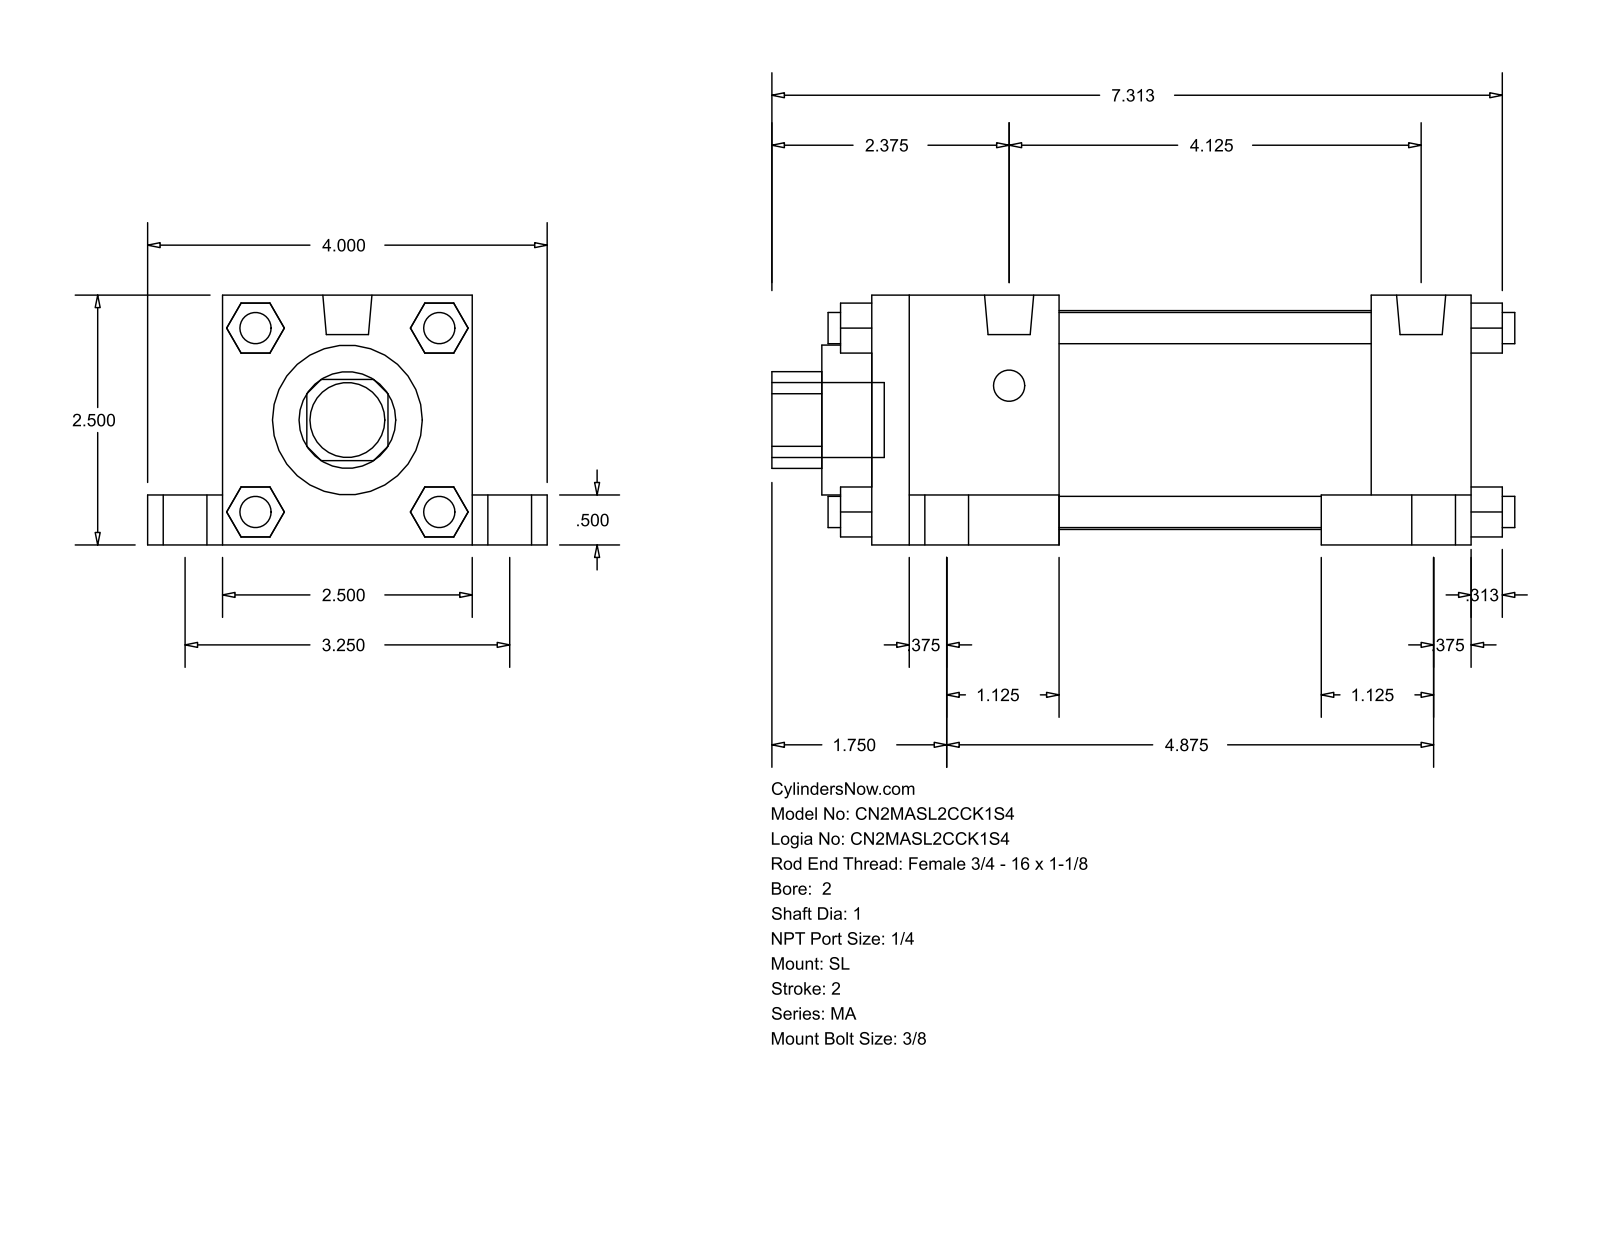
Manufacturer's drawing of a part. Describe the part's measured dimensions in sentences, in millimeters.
The part is named "MA_SL__0200_1". Its 3-D file was written by "GSSL Pune (CONFIG_CONTROL_DESIGN)". It is 0 solids with 148 faces: 112 planar, 36 cylindrical and 0 other. Overall it measures 188.91 by 101.6 by 63.5 millimeters. Round holes: 1 of diameter 25.4, 1 of diameter 38.1, 1 of diameter 55.63. Round bosses or shafts: 8 of diameter 7.94, 4 of diameter 17.46, 4 of diameter 11.11, 2 of diameter 12.49, 1 of diameter 19.05. Partial cylindrical surfaces (rounded edges, fillets, slot ends): 1 of radius 12.29. The main face-to-face distances are 63.5, 12.7, 152.4, 19.05, 82.55, 25.4, 50.8, 47.63, 104.77, 127.
